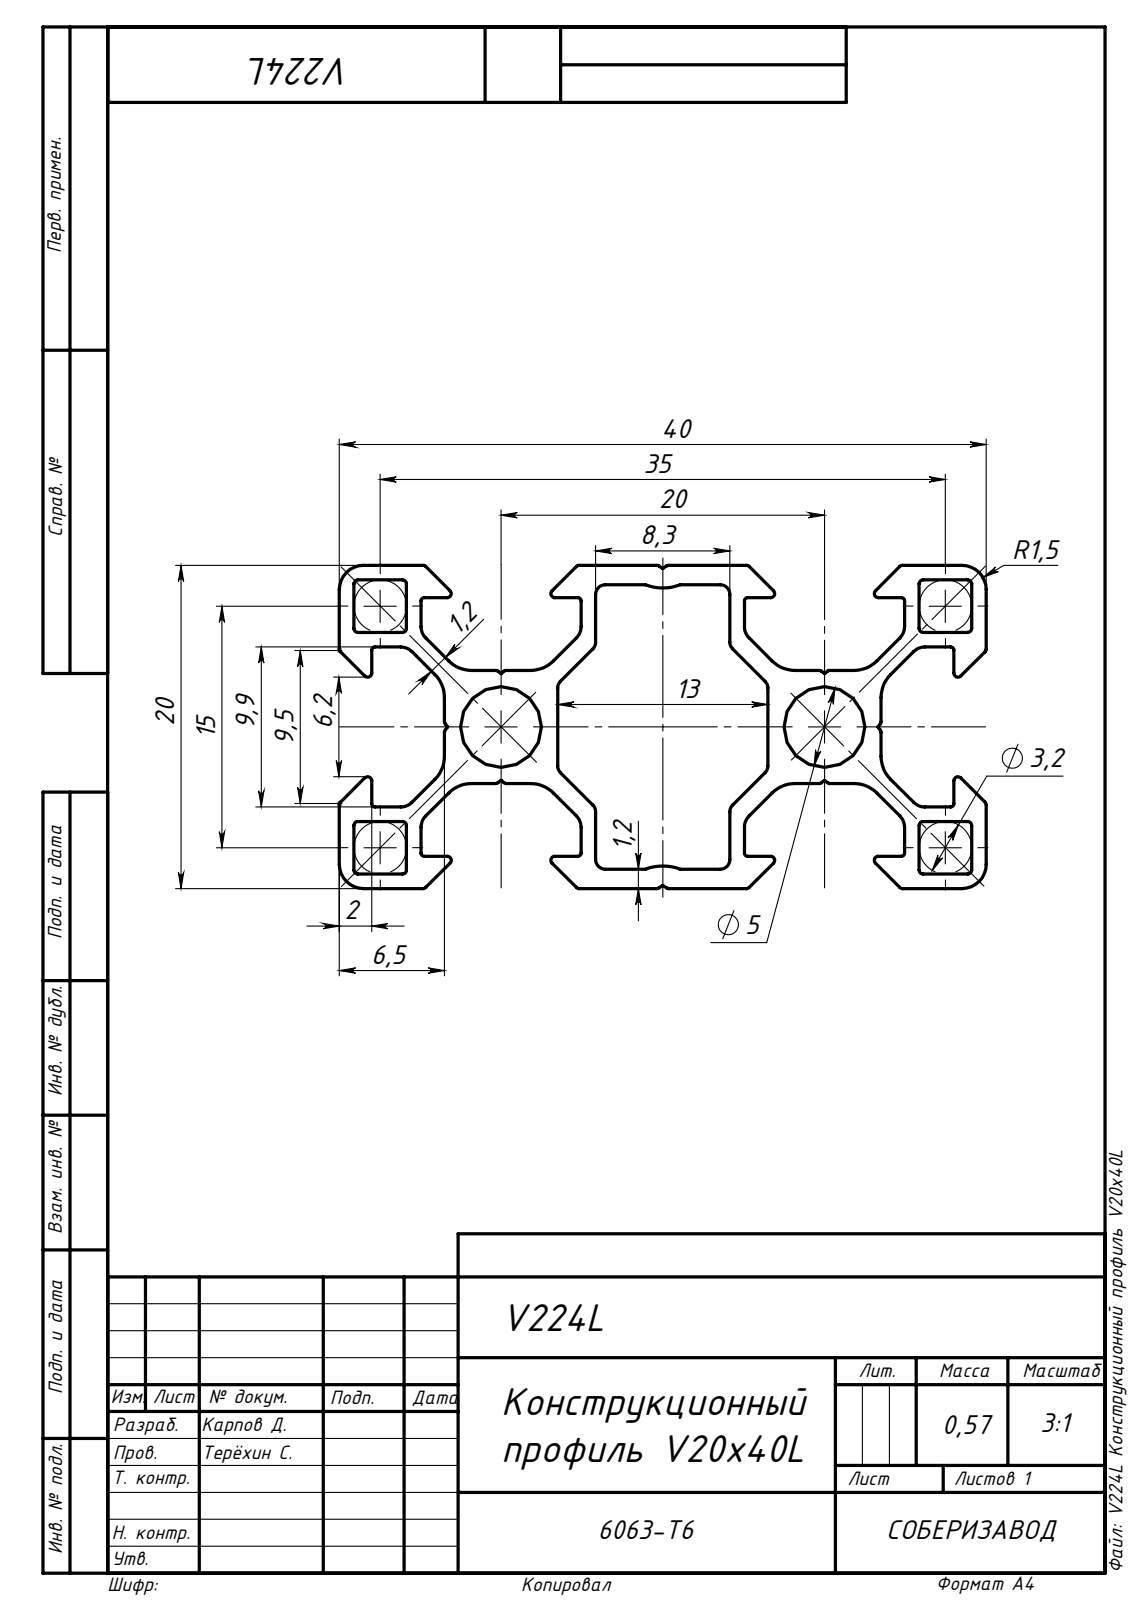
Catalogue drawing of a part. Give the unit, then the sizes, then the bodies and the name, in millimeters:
Units: millimetres
Overall size (bounding box): 1000 × 40 × 20
Partial cylindrical surfaces — rounded edges, fillets, slot ends (radius × count): R0.25 ×72, R0.2 ×12, R0.6 ×12, R1 ×12, R2 ×12, R0.7 ×8, R1.5 ×4, R2.5 ×2
Main face-to-face distances: 0.9, 3.9, 20, 14.14, 1.2, 3.13, 4.33, 11.5, 9.6, 1.1
Volume: 210 424 mm³ · Surface area: 352 402 mm²
Bodies: 1 solid, 274 faces (120 planar, 154 cylindrical, 0 other)
STEP written by: SolidWorks 2018 (AUTOMOTIVE_DESIGN)
